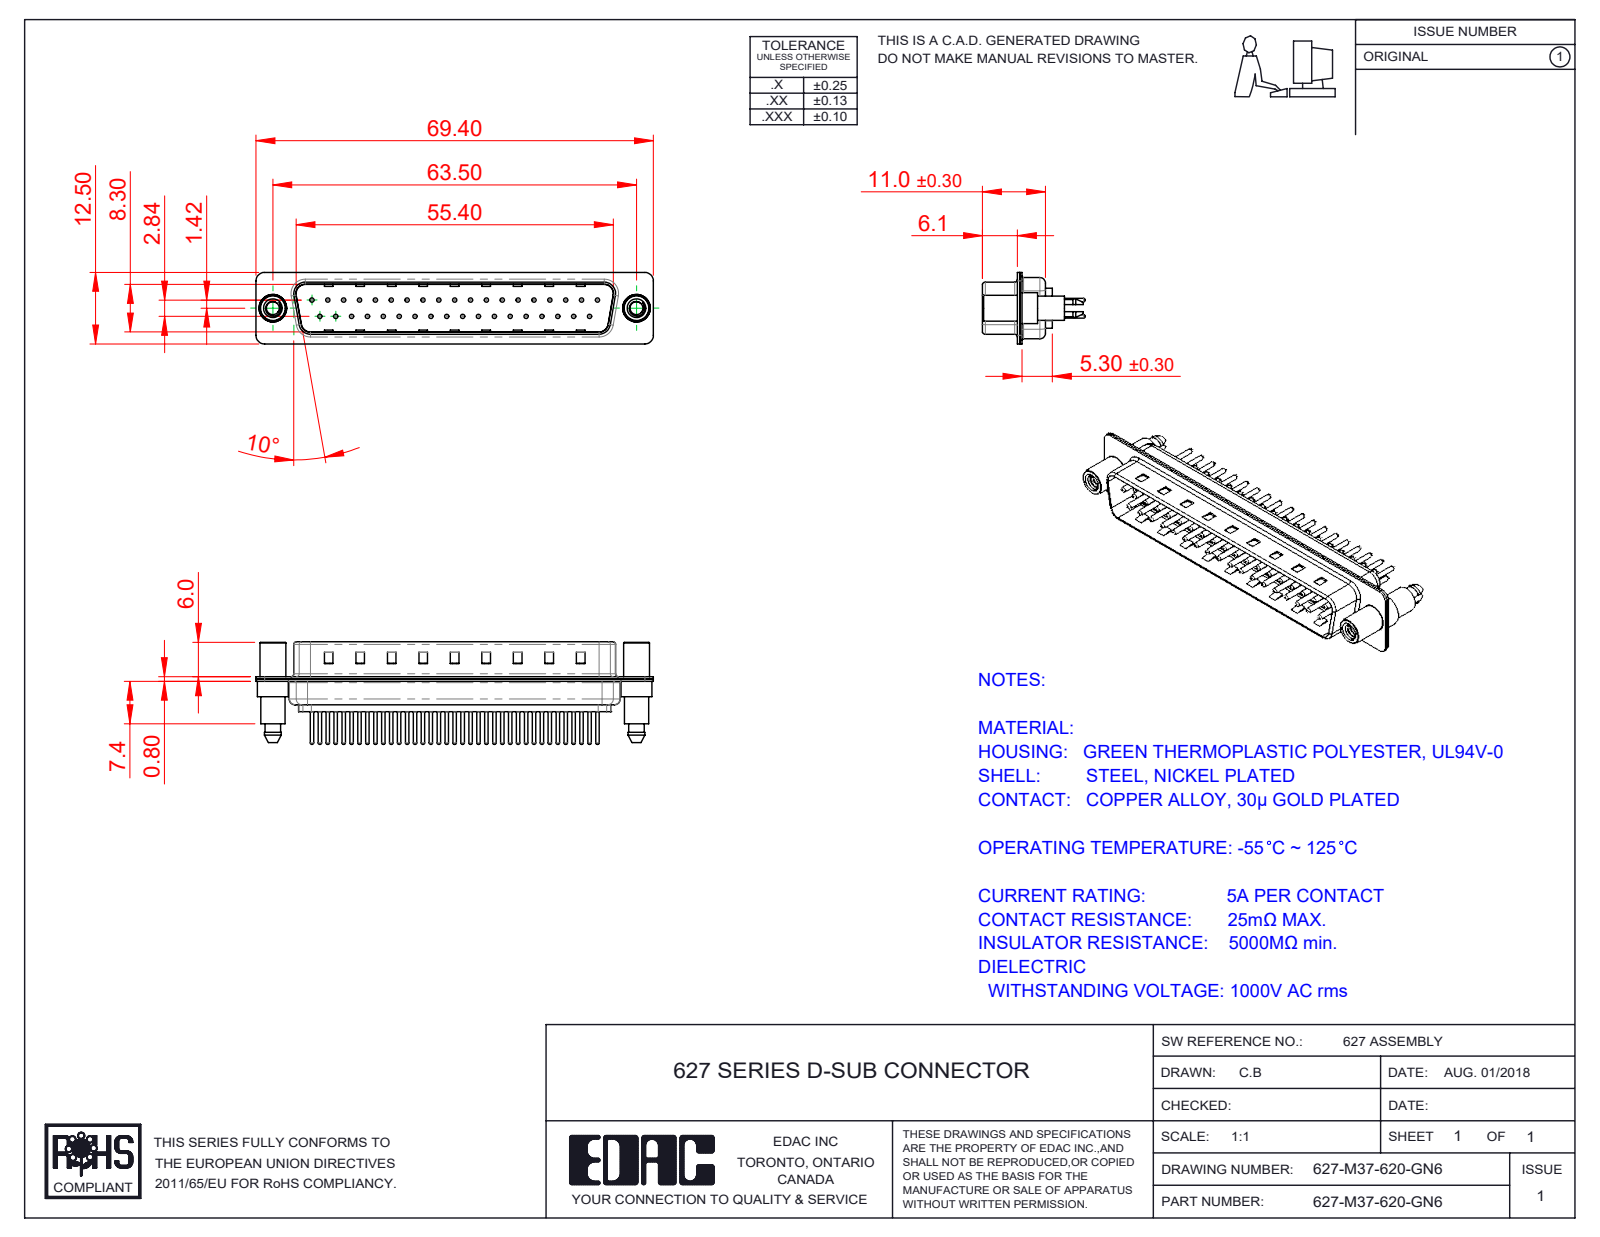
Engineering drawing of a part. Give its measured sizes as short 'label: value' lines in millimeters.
name: 627M Contact Row 1_20; 627M Shell Front_37 Contacts; 627M Shell Rear_37 Contacts; 627M Contact Row 2_20 (+3 more)
written by: SolidWorks 2020 (CONFIG_CONTROL_DESIGN)
unit: mm
bodies: 42 solids, 1833 faces (480 planar, 687 cylindrical, 666 other)
size: 69.4 × 17.9 × 12.5
volume: 4 106 mm³; area: 9 737 mm²
holes: 37× ⌀0.75, 37× ⌀1.6, 37× ⌀2, 2× ⌀2.26, 2× ⌀4, 2× ⌀4.8
bosses: 37× ⌀1.5, 37× ⌀0.6, 2× ⌀5.4, 2× ⌀4.9, 2× ⌀4.5, 2× ⌀4.25
rounds: 18× R1.5, 12× R2, 10× R1.6, 8× R0.5, 4× R0.25, 4× R0.6, 4× R0.65, 4× R0.9
face distances: 0.4, 0.8, 9.5, 9.1, 8.7, 9.9, 1.2, 5.7, 0.75, 0.35
hole spacings: 2.77, 5.54, 3.16, 8.31, 11.08, 13.85, 16.62, 19.39
